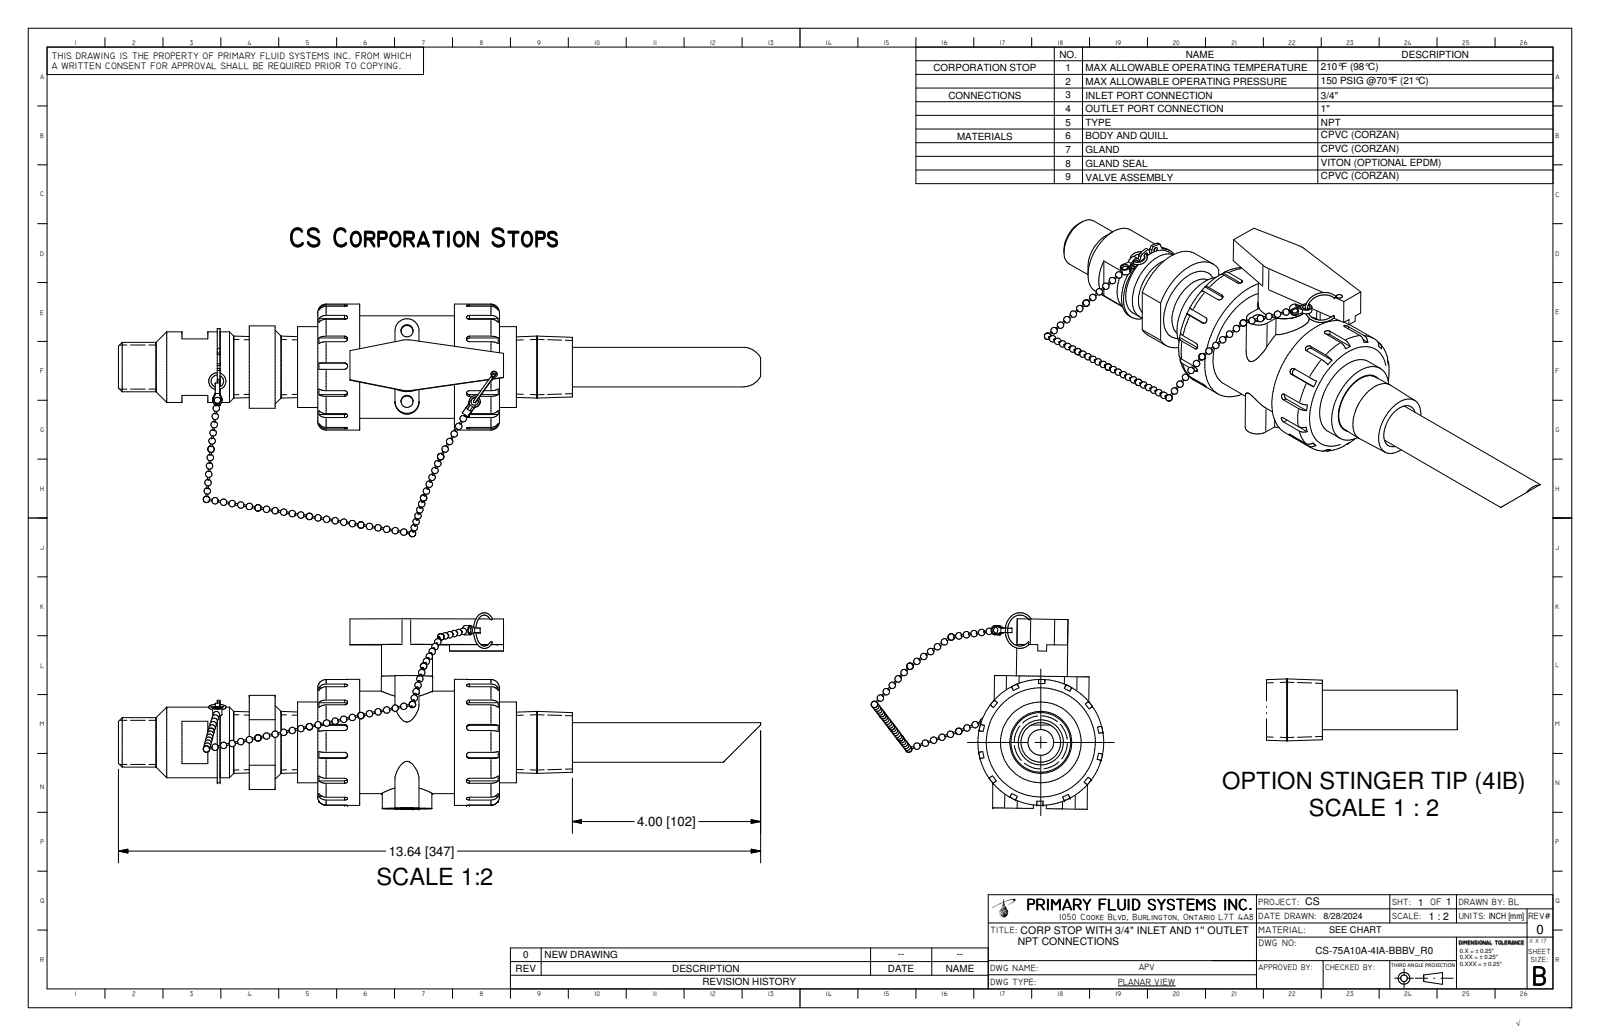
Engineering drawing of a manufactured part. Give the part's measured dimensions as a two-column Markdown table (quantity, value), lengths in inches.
| quantity | value |
| --- | --- |
| STEP written by | Autodesk Inventor 2025 (CONFIG_CONTROL_DESIGN) |
| units | inches |
| bodies | 19 solids, 420 faces (205 planar, 136 cylindrical, 79 other) |
| overall size | 13.643 × 4.94 × 4.175 |
| volume | 29.39 in³ |
| surface area | 175.1 in² |
| round holes (diameter × count) | 0.256 × 4, 0.098 × 2, 0.15 × 2, 0.157 × 2, 0.13 × 1, 0.54 × 1, 0.546 × 1, 0.818 × 1, 0.875 × 1, 0.957 × 1, 1.306 × 1, 1.315 × 1 |
| round bosses / shafts (diameter × count) | 0.035 × 9, 0.236 × 2, 2.673 × 1, 2.177 × 1, 1.713 × 1, 1.634 × 1, 1.5 × 1, 1.33 × 1 |
| partial cylindrical surfaces (radius × count) | 0.067 × 28, 0.054 × 2, 0.098 × 2, 0.197 × 2, 0.256 × 2, 0.545 × 1, 0.898 × 1, 1 × 1 |
| main face-to-face distances | 0.646, 2.661, 1.317, 3.333, 0.672, 3.979, 3.86, 2.906, 0.955, 0.89 |
| hole center spacings | 0.749, 1.498, 0.795, 1.437, 1.932, 2.076, 2.089, 0.295 |
